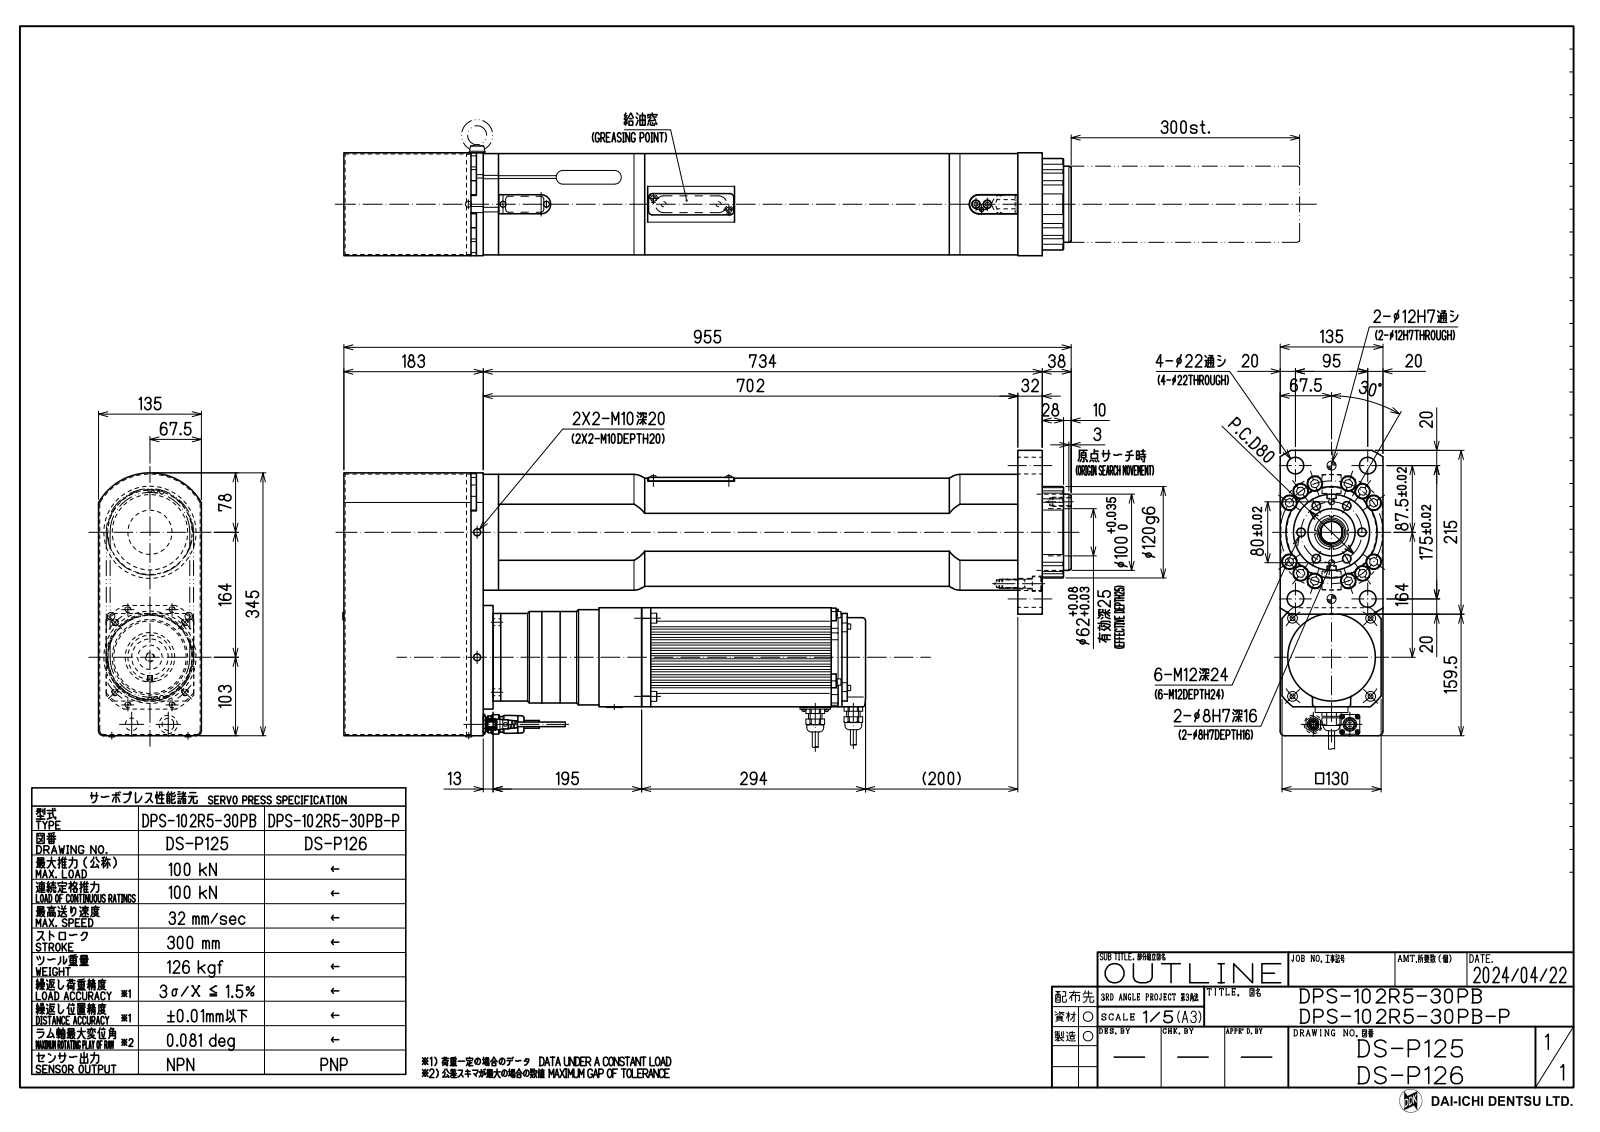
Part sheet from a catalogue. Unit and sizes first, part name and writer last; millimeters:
Units: millimetres
Overall size (bounding box): 956.5 × 388.51 × 135
Round holes (diameter × count): ⌀6.65 ×12, ⌀1 ×8, ⌀1.1 ×7, ⌀10.11 ×6, ⌀11 ×5, ⌀1.2 ×4, ⌀3.24 ×4, ⌀4.5 ×4, ⌀4.92 ×4, ⌀8 ×4, ⌀9 ×4, ⌀9.1 ×4
Round bosses / shafts (diameter × count): ⌀18 ×9, ⌀1.6 ×8, ⌀4 ×7, ⌀1.55 ×7, ⌀1 ×7, ⌀8 ×5, ⌀8.5 ×4, ⌀6 ×4
Partial cylindrical surfaces — rounded edges, fillets, slot ends (radius × count): R5 ×43, R2 ×19, R1 ×9, R2.5 ×9, R3 ×9, R10 ×6, R4 ×5, R4.25 ×4
Main face-to-face distances: 1, 3, 134, 6, 135, 9, 68, 133, 71, 65
Hole centre spacings: 3, 97.37, 5.2, 7.51, 10.26, 23.69, 24.94, 47.5
Volume: 26 180 000 mm³ · Surface area: 1 408 000 mm²
Bodies: 2 solids, 1684 faces (911 planar, 405 cylindrical, 368 other)
Part name (STEP PRODUCT): DPS-102R5-30PB(-P)(DS-P125_P126)_OUTLINE; DPS-102R5-30PB(DS-P125)_BODY; DPS-102(300st)_SHAFT
STEP written by: Autodesk Inventor 2023 (CONFIG_CONTROL_DESIGN)
